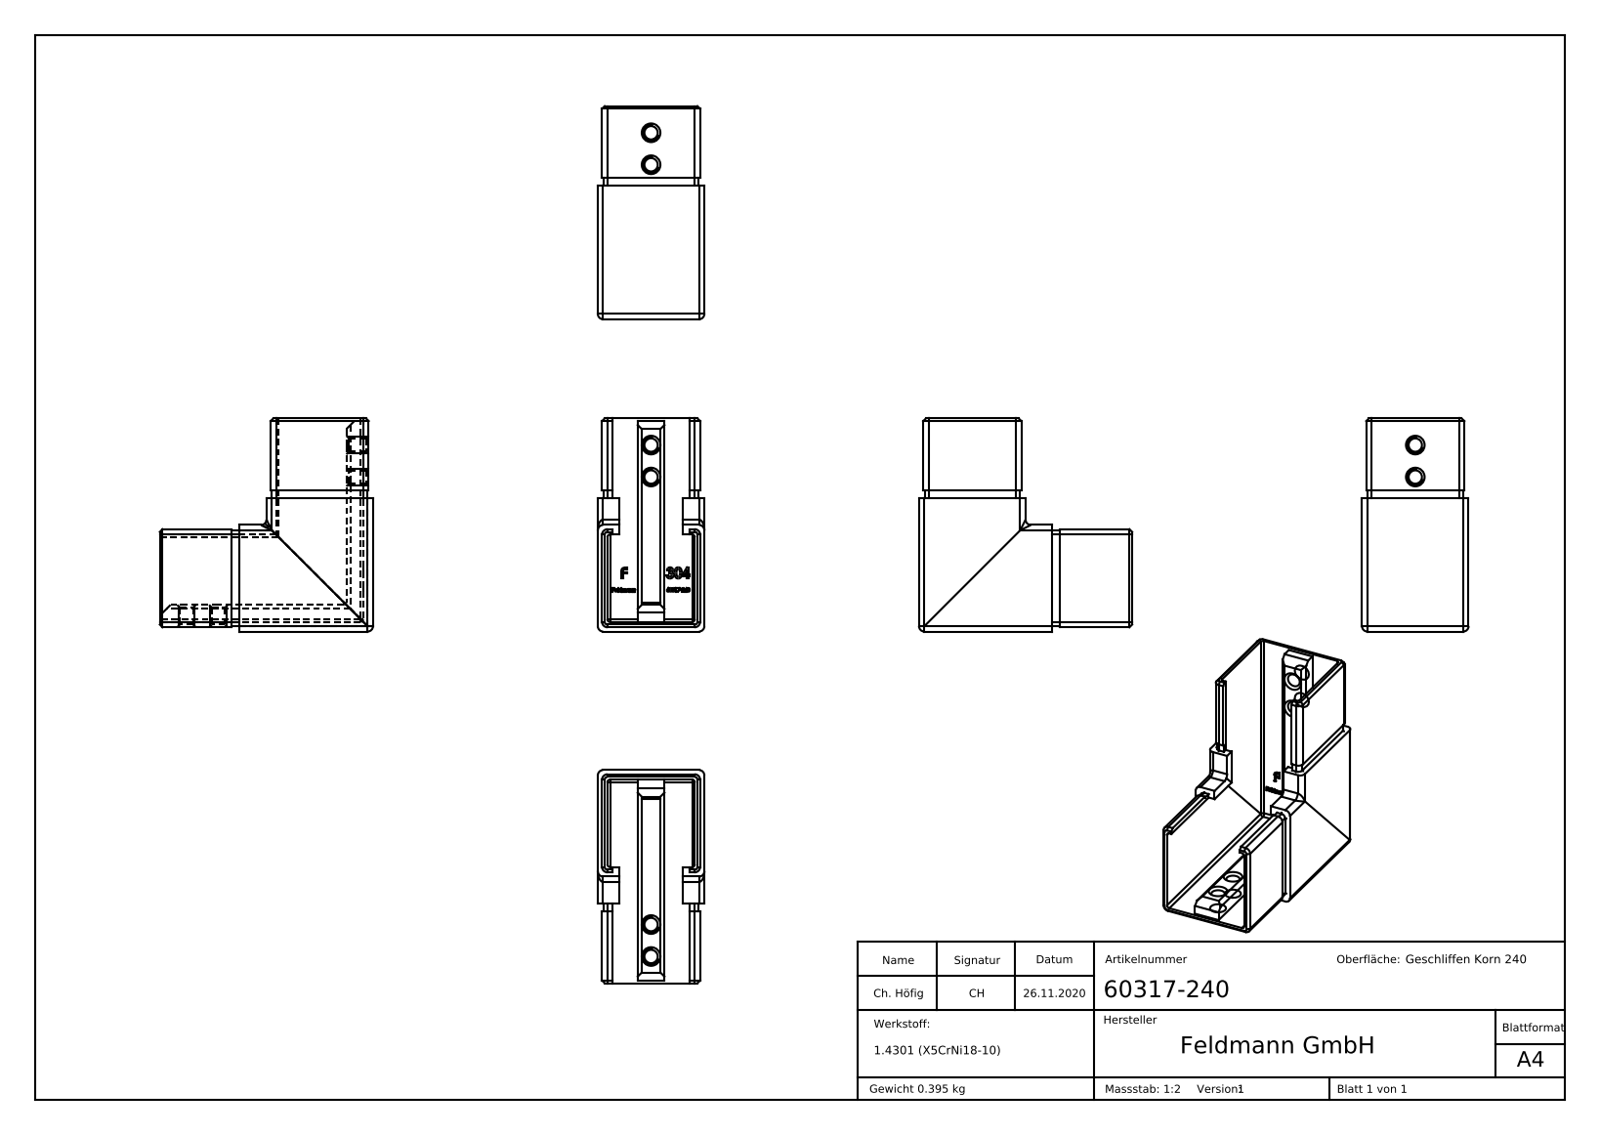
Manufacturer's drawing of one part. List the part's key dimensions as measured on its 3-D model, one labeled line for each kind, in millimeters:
Part name (STEP PRODUCT): 60317-240
STEP written by: SolidWorks 2018 (CONFIG_CONTROL_DESIGN)
Units: millimetres
Bodies: 1 solid, 446 faces (250 planar, 46 cylindrical, 150 other)
Overall size (bounding box): 80 × 80 × 40
Volume: 49 975 mm³ · Surface area: 32 115 mm²
Round holes (diameter × count): ⌀5 ×4
Partial cylindrical surfaces — rounded edges, fillets, slot ends (radius × count): R2 ×18, R1 ×10, R1.5 ×8
Main face-to-face distances: 3.6, 2, 1.6, 36.4, 32.8, 34.8, 38.4, 40, 36.8, 10
Hole centre spacings: 12
